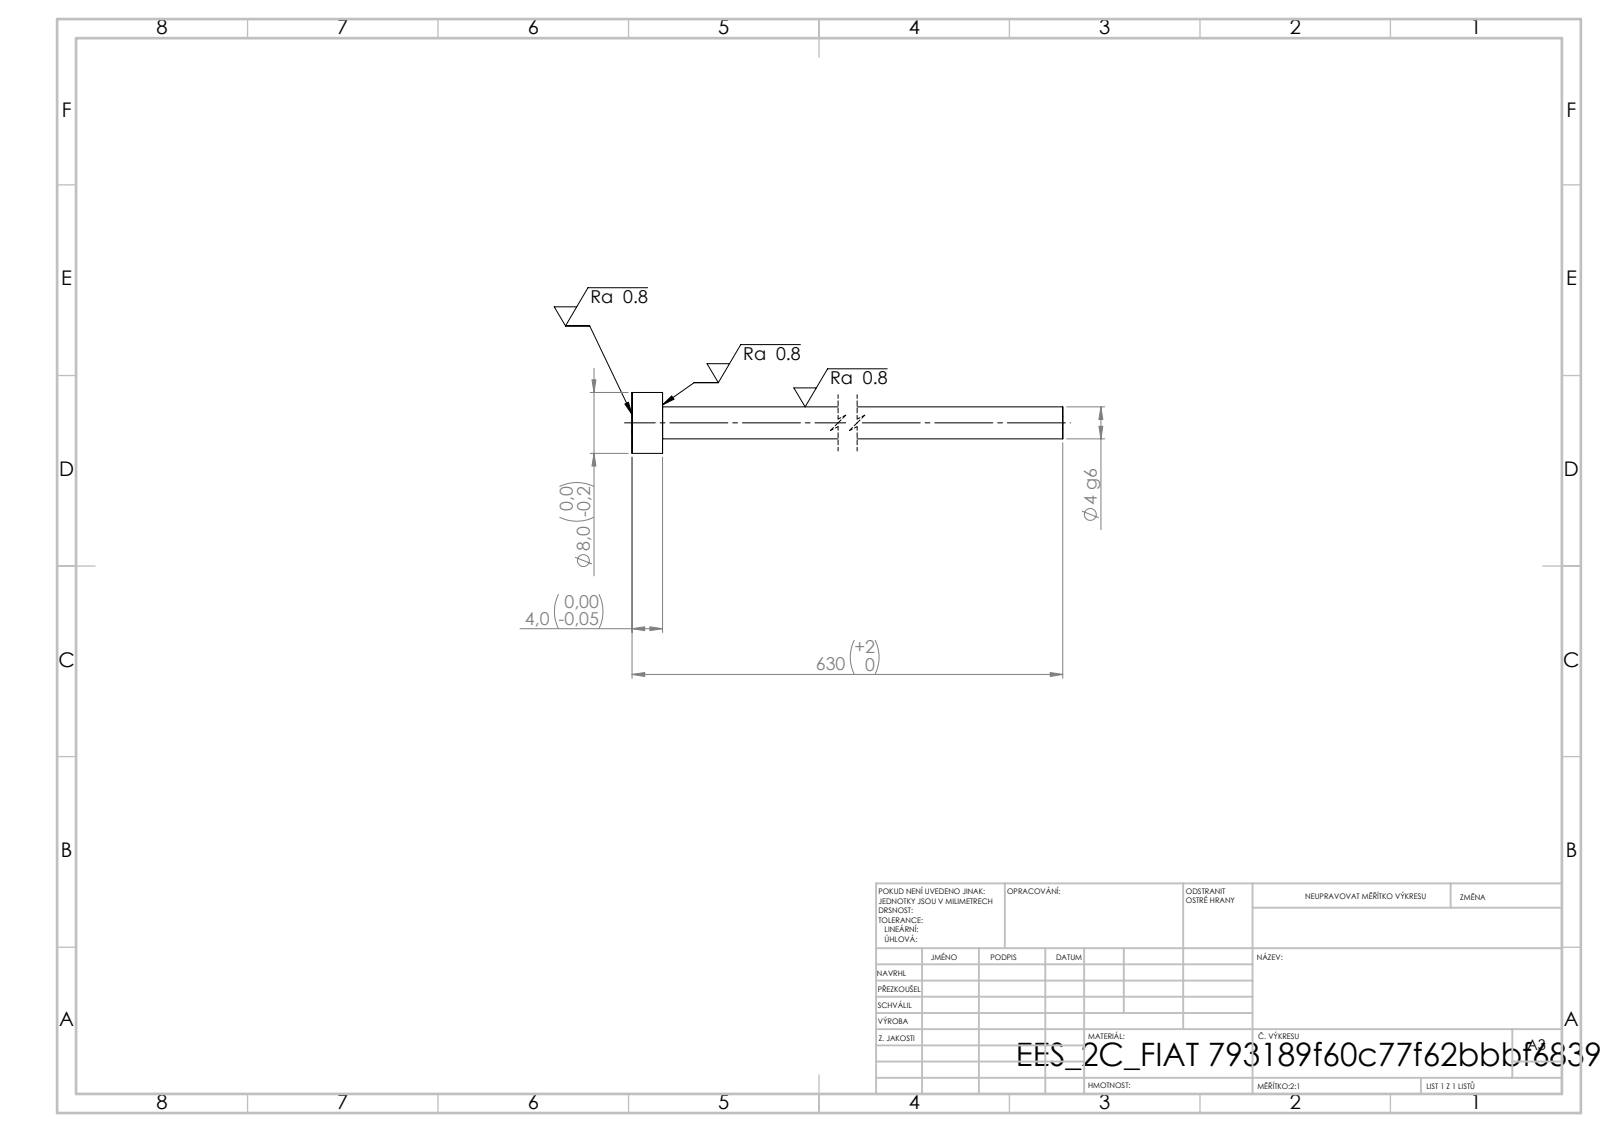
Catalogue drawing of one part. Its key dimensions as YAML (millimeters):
step_written_by: "SolidWorks 2019 (CONFIG_CONTROL_DESIGN)"
units: millimeters
bodies: {solids: 1, faces: 7, planar: 3, cylindrical: 4, other: 0}
overall_size: [630, 8, 8]
volume: 8874
surface_area: 8461
round_bosses_or_shafts:
  - {diameter: 8, count: 1}
  - {diameter: 4.2, count: 1}
face_to_face_distances: [4, 630, 626]
